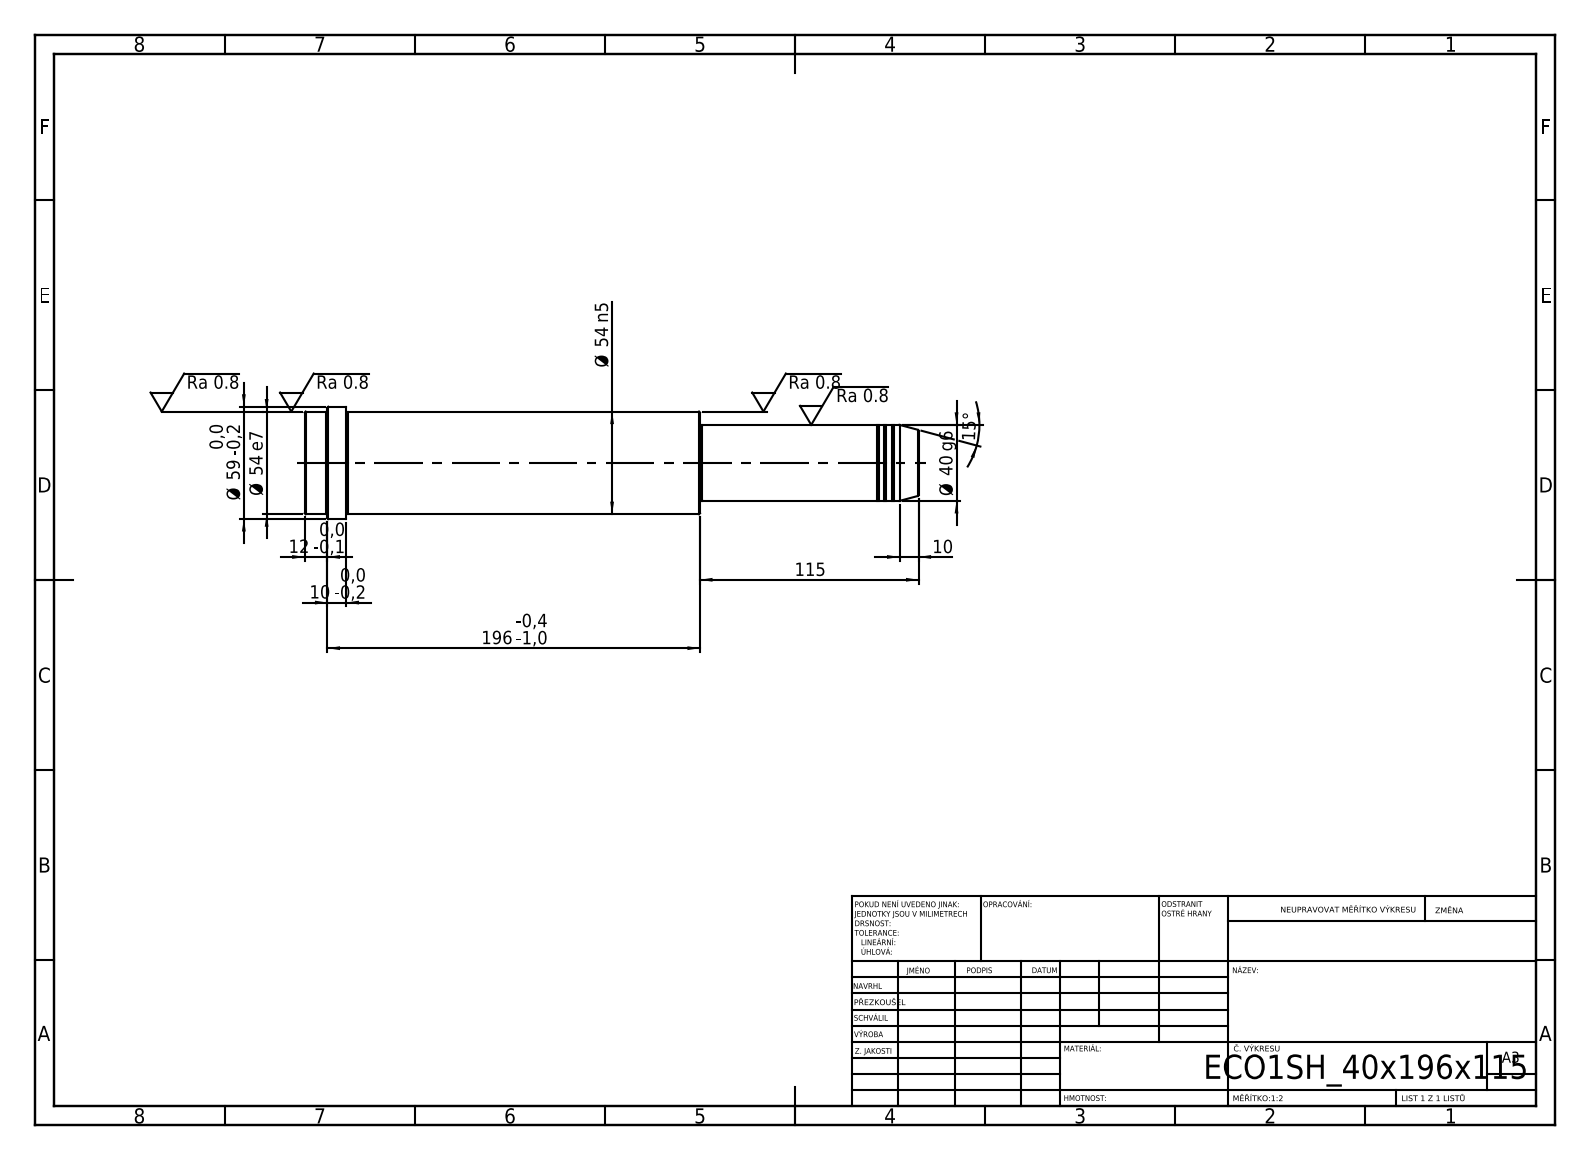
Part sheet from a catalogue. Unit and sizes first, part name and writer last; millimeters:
Units: millimetres
Overall size (bounding box): 323 × 59 × 59
Round bosses / shafts (diameter × count): ⌀59 ×1, ⌀54 ×1, ⌀40 ×1, ⌀39 ×1
Main face-to-face distances: 208, 115, 323, 301, 186, 22, 311, 196, 10, 12
Volume: 623 299 mm³ · Surface area: 55 353 mm²
Bodies: 1 solid, 52 faces (6 planar, 16 cylindrical, 30 other)
STEP written by: SolidWorks 2019 (CONFIG_CONTROL_DESIGN)
